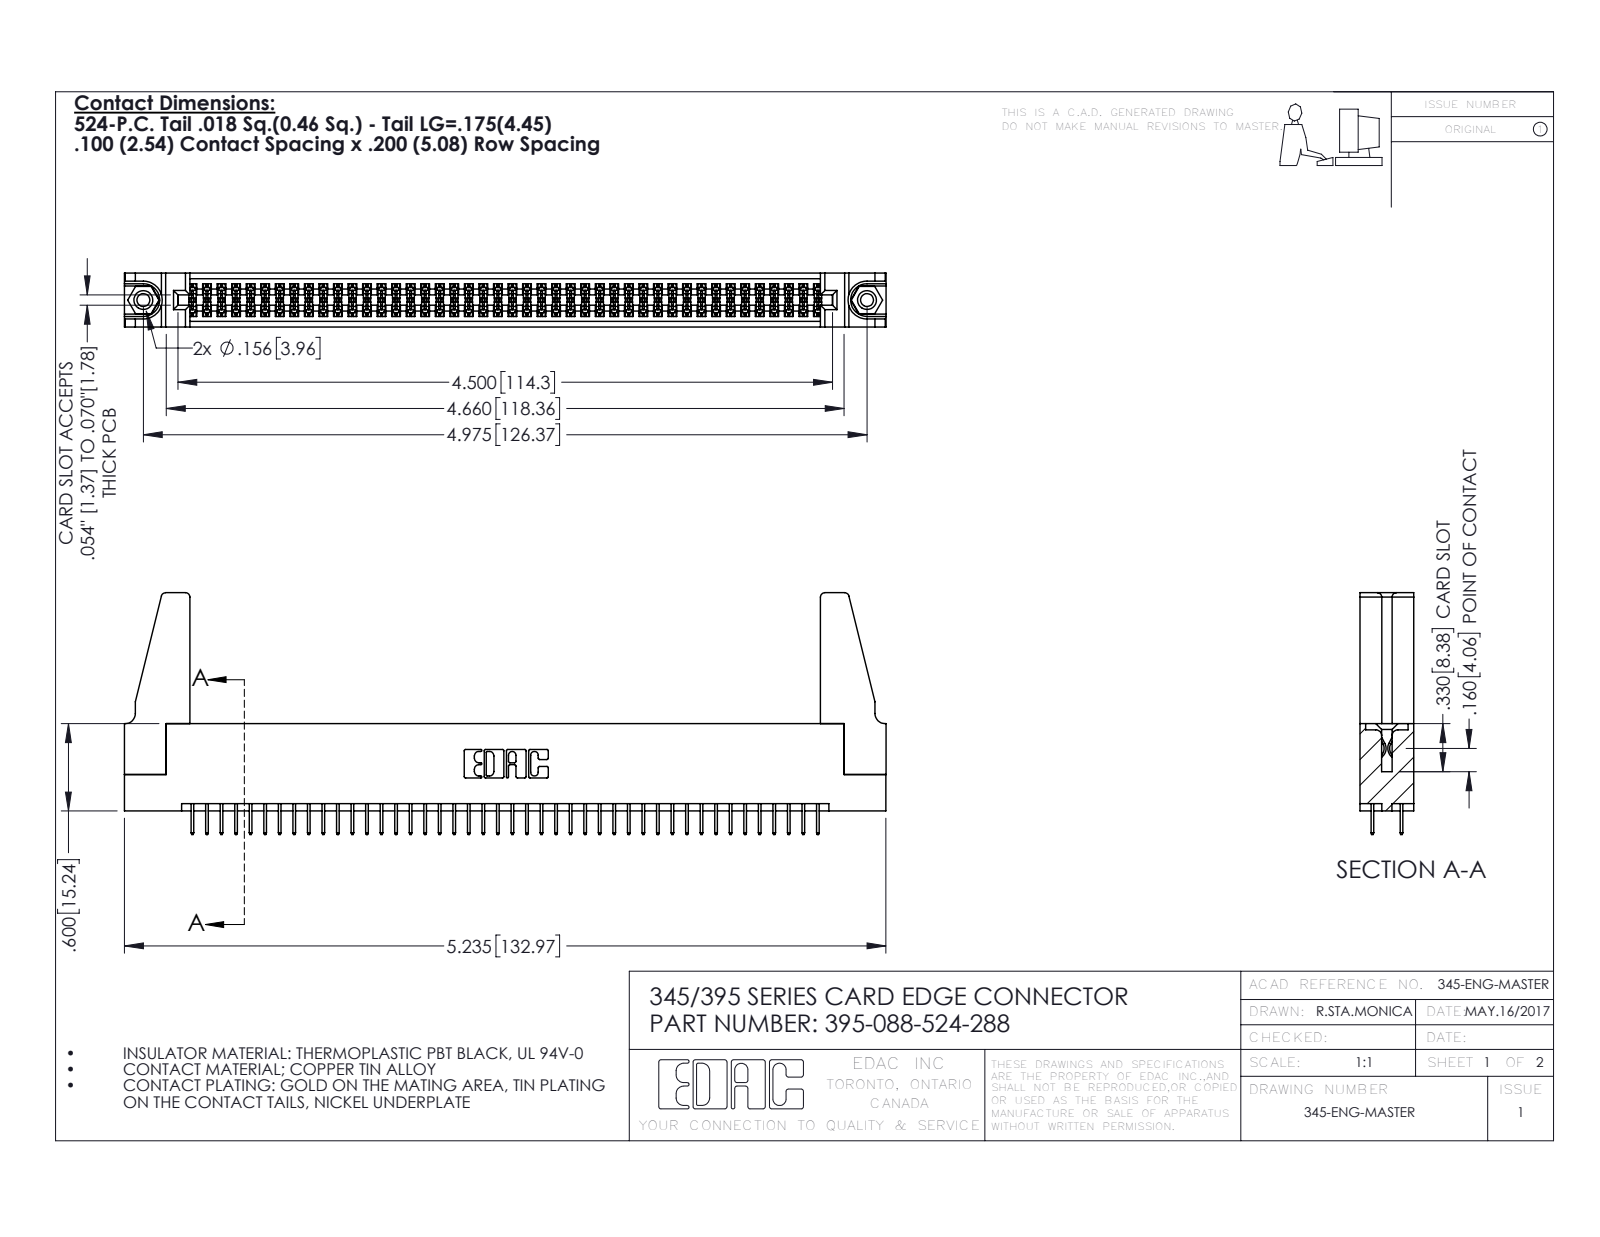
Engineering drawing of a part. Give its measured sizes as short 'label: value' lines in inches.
name: 345 Part_Flush Mounting Lugs - 0.156 Dia-TH; 345-250-001_345-250-001-102; 345-220-078_345-220-088; 395-088-524-288 (+1 more)
written by: SolidWorks 2016 (CONFIG_CONTROL_DESIGN)
unit: in
bodies: 93 solids, 5002 faces (3584 planar, 1402 cylindrical, 16 other)
size: 5.236 × 1.662 × 0.37
volume: 0.98 in³; area: 33.69 in²
holes: 2× ⌀0.089, 2× ⌀0.125, 2× ⌀0.156, 1× ⌀0.064
bosses: 2× ⌀0.155
rounds: 132× R0.006, 22× R0.01, 8× R0.03, 6× R0.007, 6× R0.031, 3× R0.026, 2× R0.014, 2× R0.019
face distances: 0.072, 0.298, 0.37, 0.2, 0.098, 0.272, 0.025, 0.225, 0.072, 0.175
hole spacings: 0.27, 4.739, 4.975
